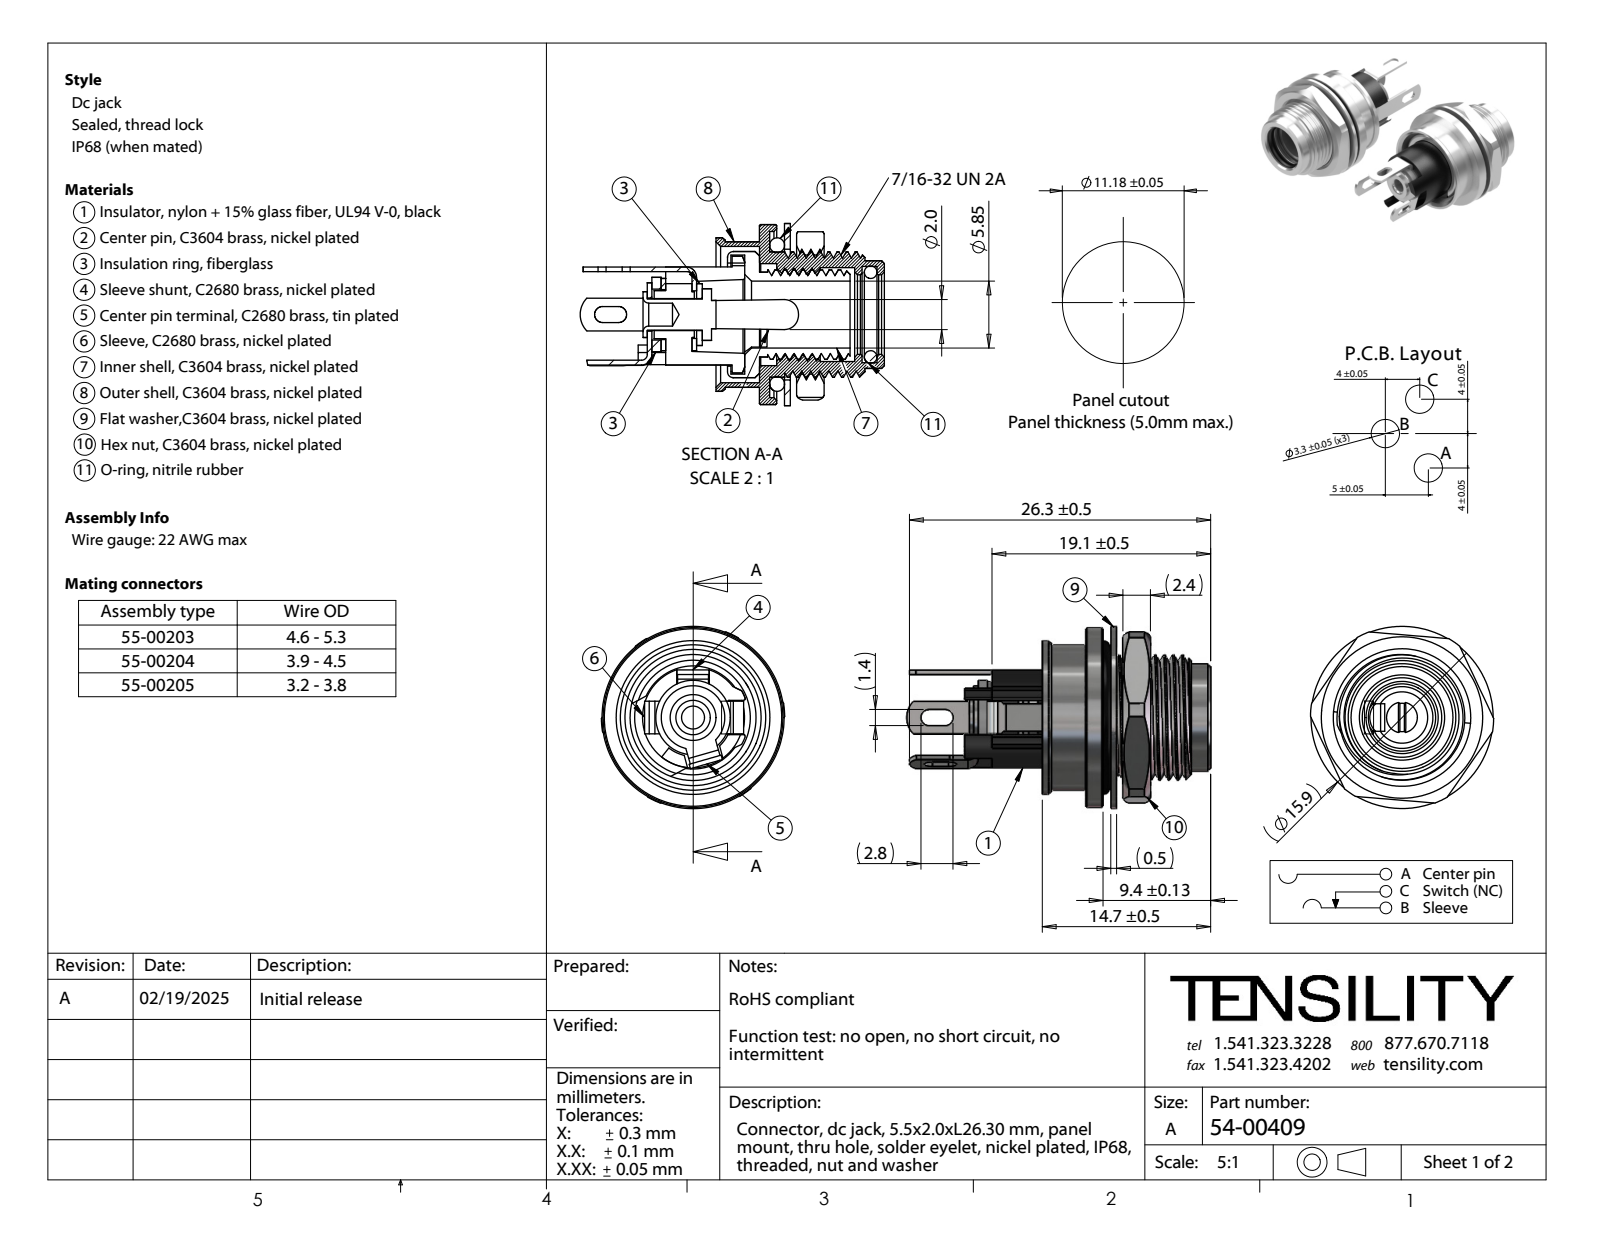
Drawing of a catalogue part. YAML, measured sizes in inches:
part_name: "大防水胶圈; 铜垫片; 玻璃纤维大垫片; ДёДЪЦчМе (+4 more)"
step_written_by: "SolidWorks 2016 (CONFIG_CONTROL_DESIGN)"
units: inches
bodies: {solids: 14, faces: 427, planar: 131, cylindrical: 187, other: 109}
overall_size: [1.045, 0.63, 0.626]
volume: 0.09
surface_area: 6.687
round_holes:
  - {diameter: 0.079, count: 1}
  - {diameter: 0.11, count: 1}
  - {diameter: 0.114, count: 1}
  - {diameter: 0.164, count: 1}
  - {diameter: 0.172, count: 1}
  - {diameter: 0.175, count: 1}
  - {diameter: 0.23, count: 1}
  - {diameter: 0.274, count: 1}
  - {diameter: 0.28, count: 1}
  - {diameter: 0.323, count: 1}
  - {diameter: 0.331, count: 1}
  - {diameter: 0.35, count: 1}
round_bosses_or_shafts:
  - {diameter: 0.626, count: 1}
  - {diameter: 0.618, count: 1}
  - {diameter: 0.528, count: 1}
  - {diameter: 0.5, count: 1}
  - {diameter: 0.433, count: 1}
  - {diameter: 0.431, count: 1}
  - {diameter: 0.402, count: 1}
  - {diameter: 0.37, count: 1}
partial_cylinders:
  - {radius: 0.028, count: 6}
  - {radius: 0.02, count: 5}
  - {radius: 0.035, count: 5}
  - {radius: 0.081, count: 3}
  - {radius: 0.006, count: 2}
  - {radius: 0.016, count: 2}
  - {radius: 0.043, count: 2}
  - {radius: 0.01, count: 1}
face_to_face_distances: [0.016, 0.051, 0.086, 0.106, 0.02, 0.047, 0.035, 0.322, 0.035, 0.154]
